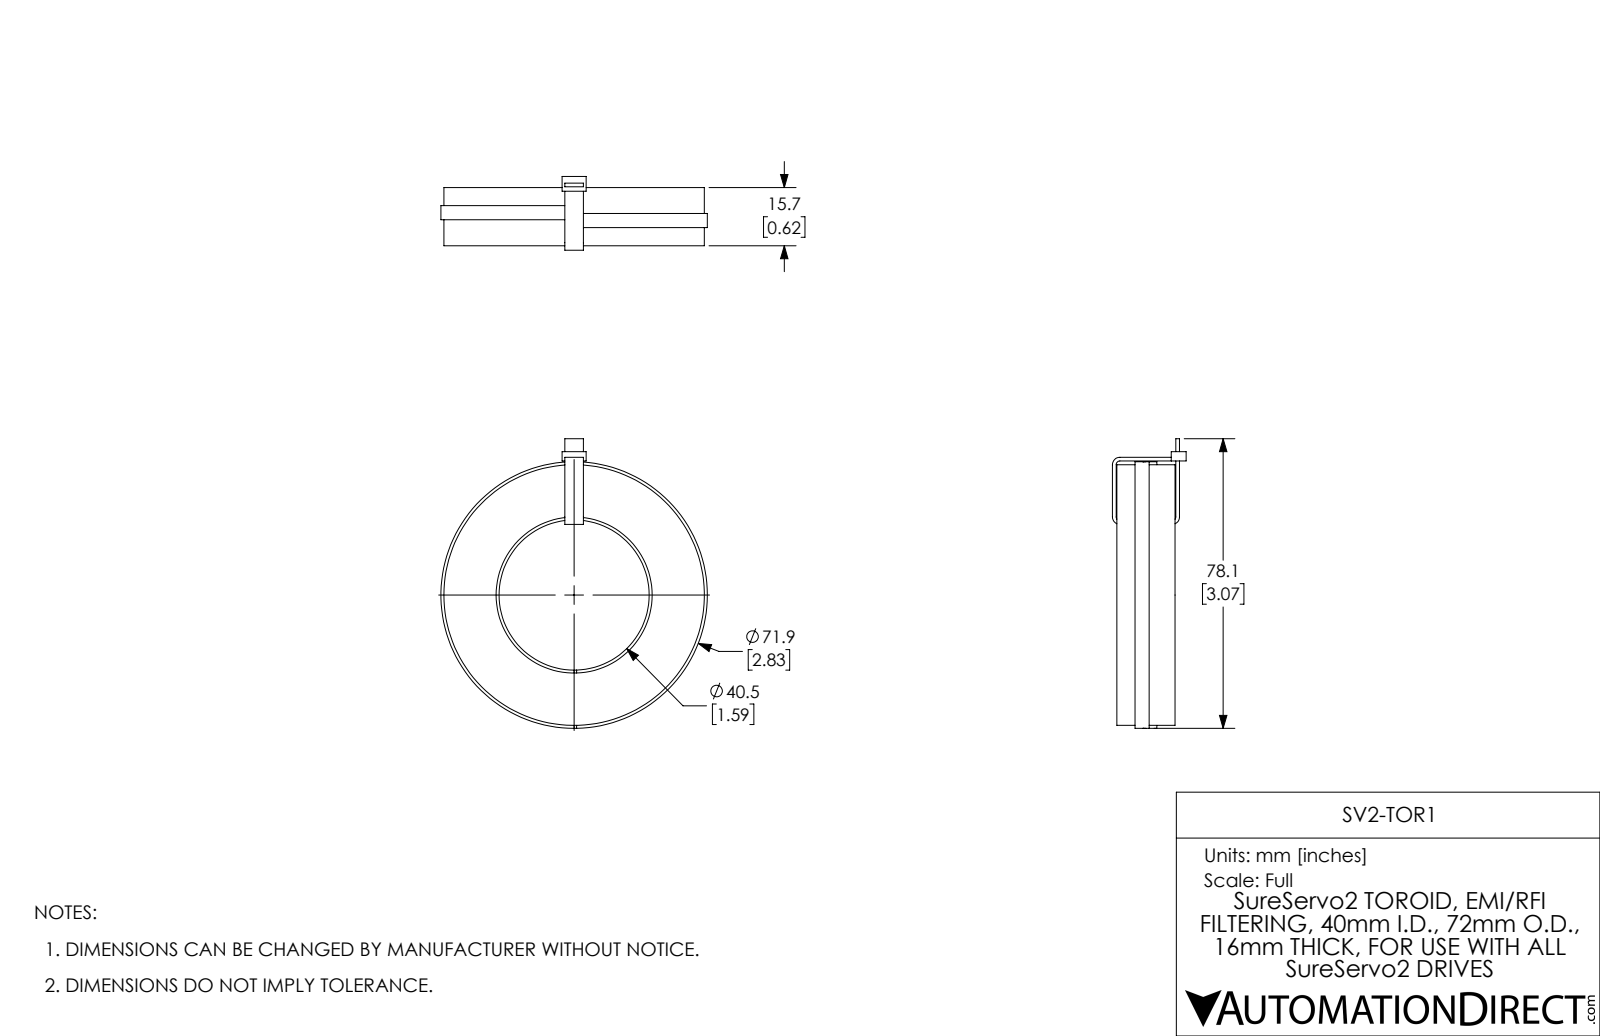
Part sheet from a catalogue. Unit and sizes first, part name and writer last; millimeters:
Units: millimetres
Overall size (bounding box): 78.1 × 71.9 × 19.9
Round holes (diameter × count): ⌀40.5 ×1, ⌀42.1 ×1, ⌀44 ×1, ⌀68.7 ×1
Round bosses / shafts (diameter × count): ⌀71.9 ×1, ⌀70.3 ×1, ⌀68 ×1, ⌀43.7 ×1
Partial cylindrical surfaces — rounded edges, fillets, slot ends (radius × count): R1 ×3, R2 ×3
Main face-to-face distances: 0.8, 14.9, 1.1, 14.6, 13.8, 15.7, 14.1, 13.5, 7, 7.9
Volume: 37 620 mm³ · Surface area: 32 290 mm²
Bodies: 4 solids, 88 faces (50 planar, 34 cylindrical, 4 other)
Part name (STEP PRODUCT): core SV2-TOR1
STEP written by: SolidWorks 2017 (AUTOMOTIVE_DESIGN)
